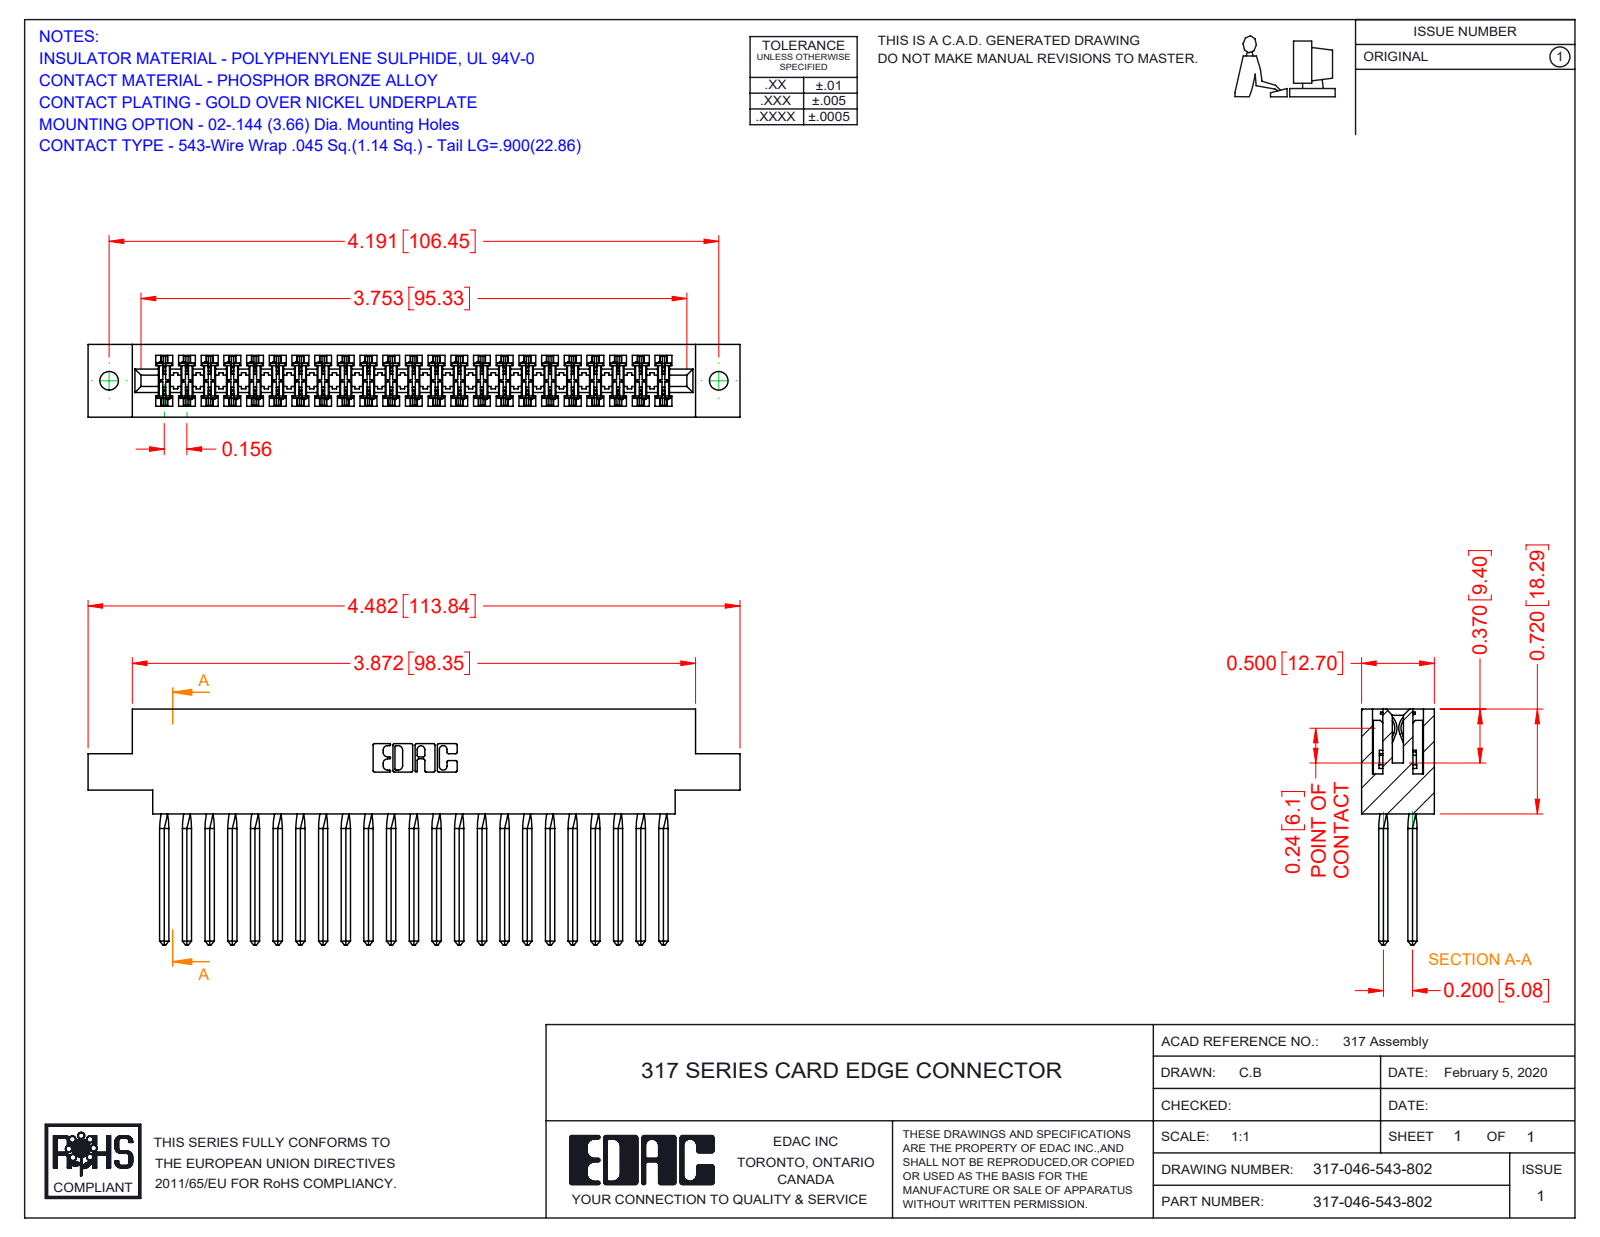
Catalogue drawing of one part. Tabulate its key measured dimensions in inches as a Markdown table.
| quantity | value |
| --- | --- |
| part name | 317-046-543-802; 317 Part_.144 Dia; 317-290-001_543 |
| STEP written by | SolidWorks 2016 (CONFIG_CONTROL_DESIGN) |
| units | inches |
| bodies | 47 solids, 4196 faces (3416 planar, 596 cylindrical, 184 other) |
| overall size | 4.482 × 1.62 × 0.5 |
| volume | 1.138 in³ |
| surface area | 42.3 in² |
| round holes (diameter × count) | 0.128 × 2 |
| partial cylindrical surfaces (radius × count) | 0.015 × 92, 0.01 × 22, 0.007 × 6, 0.031 × 6, 0.026 × 3, 0.095 × 2, 0.1 × 2, 0.11 × 2 |
| main face-to-face distances | 0.5, 0.075, 0.425, 0.11, 0.35, 0.195, 0.22, 0.094, 0.72, 0.2 |
| hole center spacings | 4.191 |
